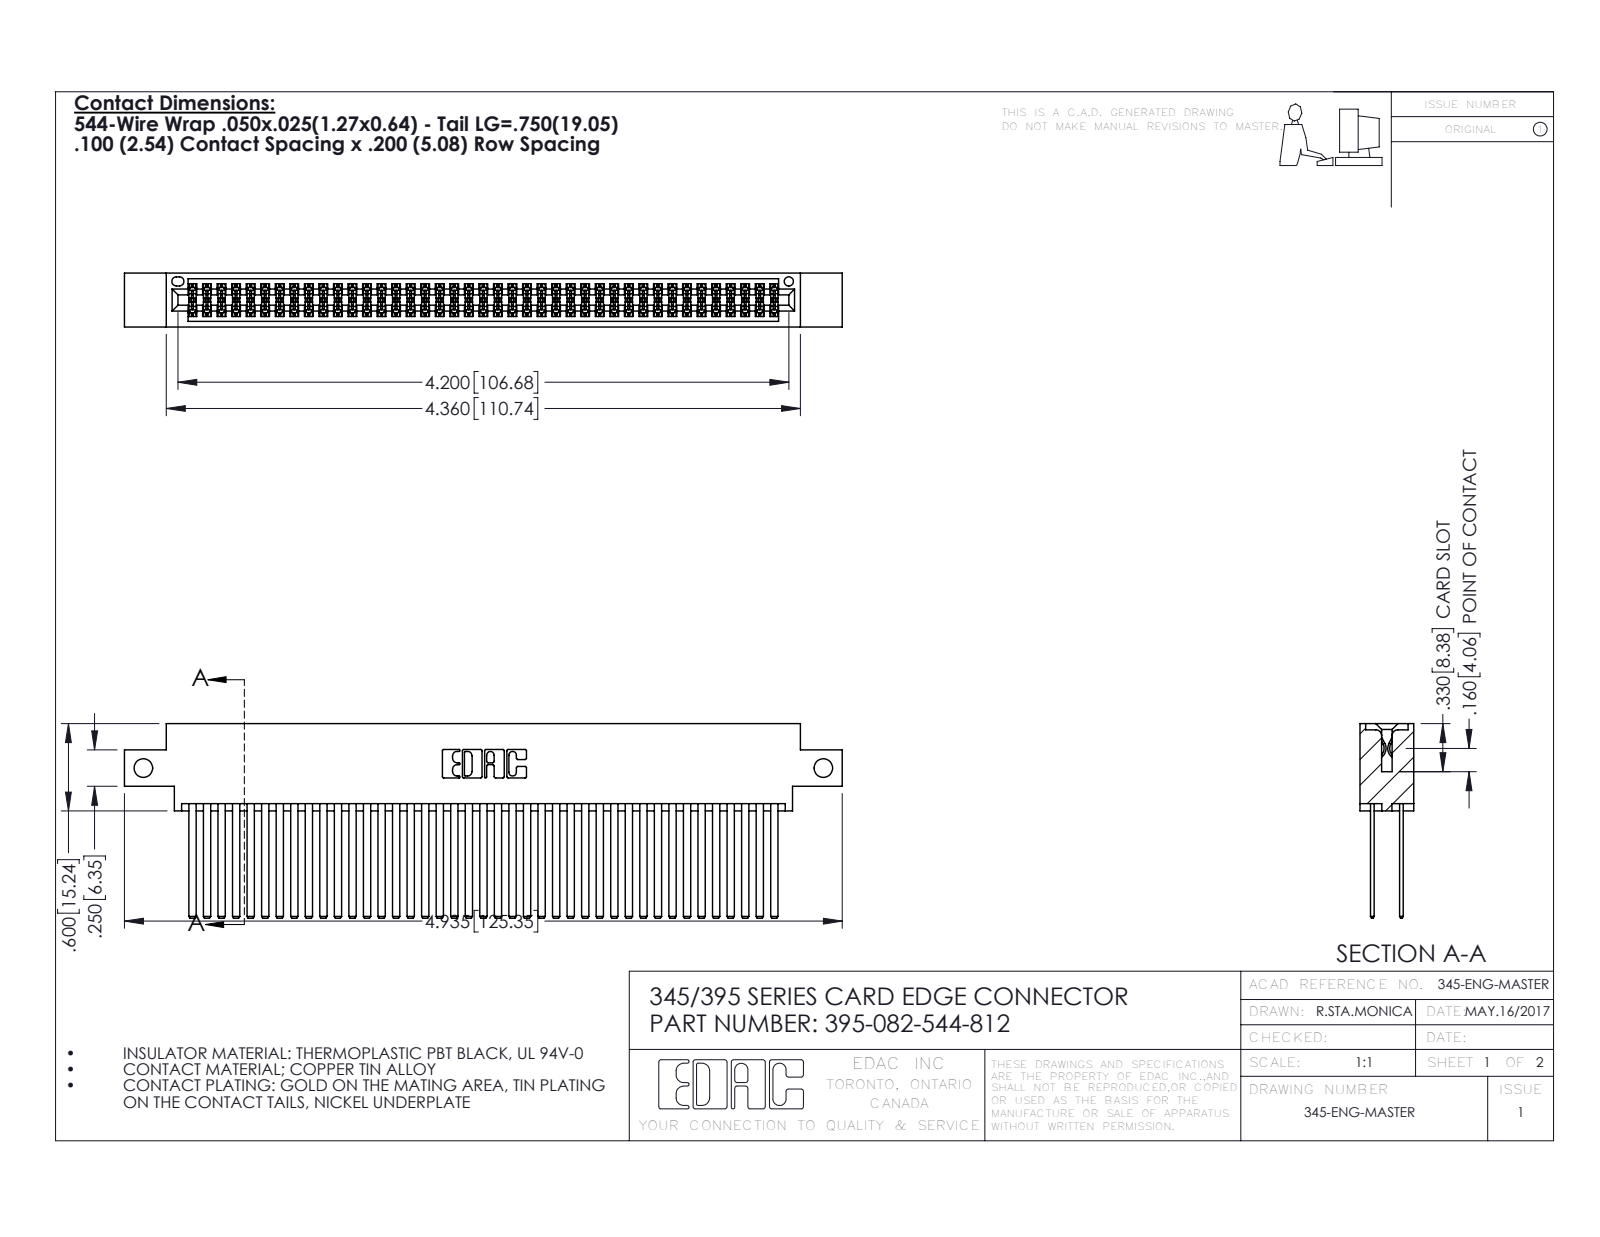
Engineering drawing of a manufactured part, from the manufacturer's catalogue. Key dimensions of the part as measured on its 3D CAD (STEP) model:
Part name (STEP PRODUCT): 345-292-001_345-293-144; 345 Part_0.170 Offset - Side Mount; 395-082-544-812
STEP written by: SolidWorks 2016 (CONFIG_CONTROL_DESIGN)
Units: inches
Bodies: 83 solids, 3738 faces (2462 planar, 1276 cylindrical, 0 other)
Overall size (bounding box): 4.935 × 1.337 × 0.37
Volume: 0.8 in³ · Surface area: 35.26 in²
Round holes (diameter × count): ⌀0.128 ×2, ⌀0.064 ×1
Partial cylindrical surfaces — rounded edges, fillets, slot ends (radius × count): R0.006 ×123, R0.01 ×22, R0.007 ×6, R0.031 ×6, R0.026 ×3, R0.014 ×2, R0.019 ×2, R0.022 ×2
Main face-to-face distances: 0.2, 0.025, 0.072, 0.098, 0.272, 0.298, 0.225, 0.175, 0.37, 0.15
Hole centre spacings: 4.675
